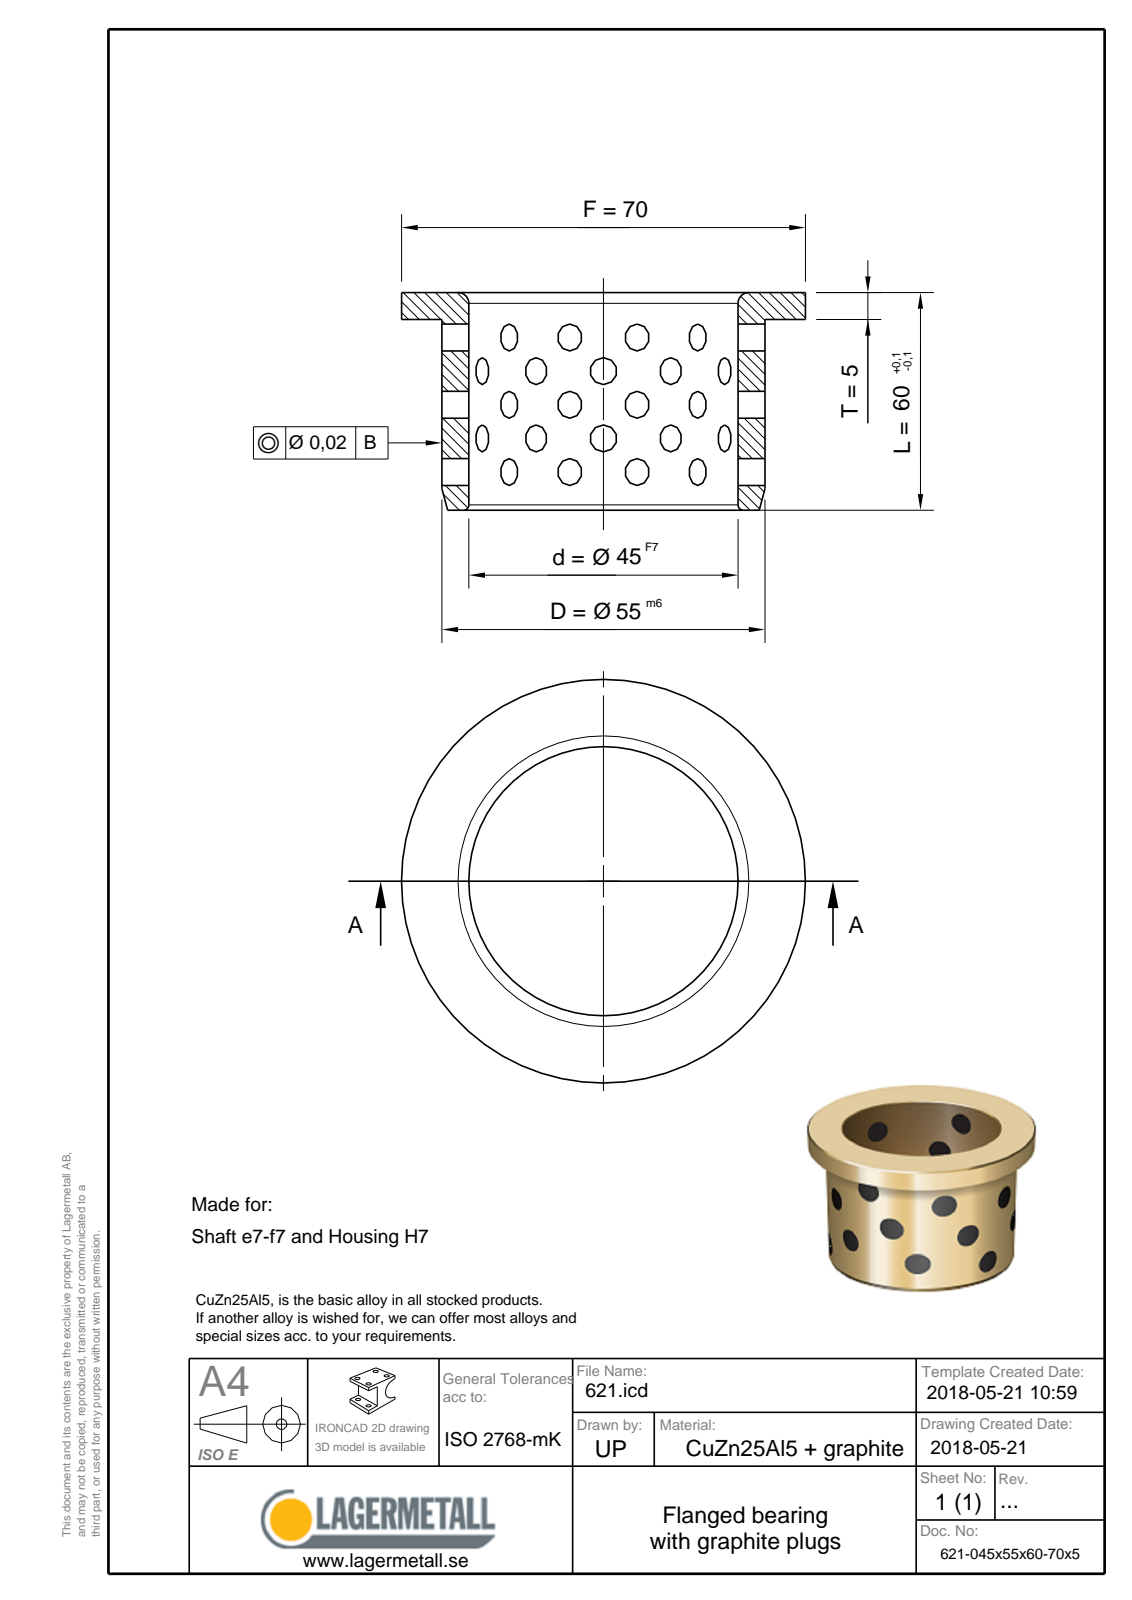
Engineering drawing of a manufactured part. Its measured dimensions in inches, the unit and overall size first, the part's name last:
Units: inches
Overall size (bounding box): 2.756 × 2.756 × 2.362
Round holes (diameter × count): ⌀1.772 ×1
Round bosses / shafts (diameter × count): ⌀2.756 ×1, ⌀2.165 ×1
Main face-to-face distances: 0.197, 2.165, 2.362
Volume: 3.297 in³ · Surface area: 36.02 in²
Bodies: 1 solid, 9 faces (3 planar, 3 cylindrical, 3 other)
Part name (STEP PRODUCT): 621-045x55x60-70x5
STEP written by: Spatial InterOp 3D (CONFIG_CONTROL_DESIGN)
